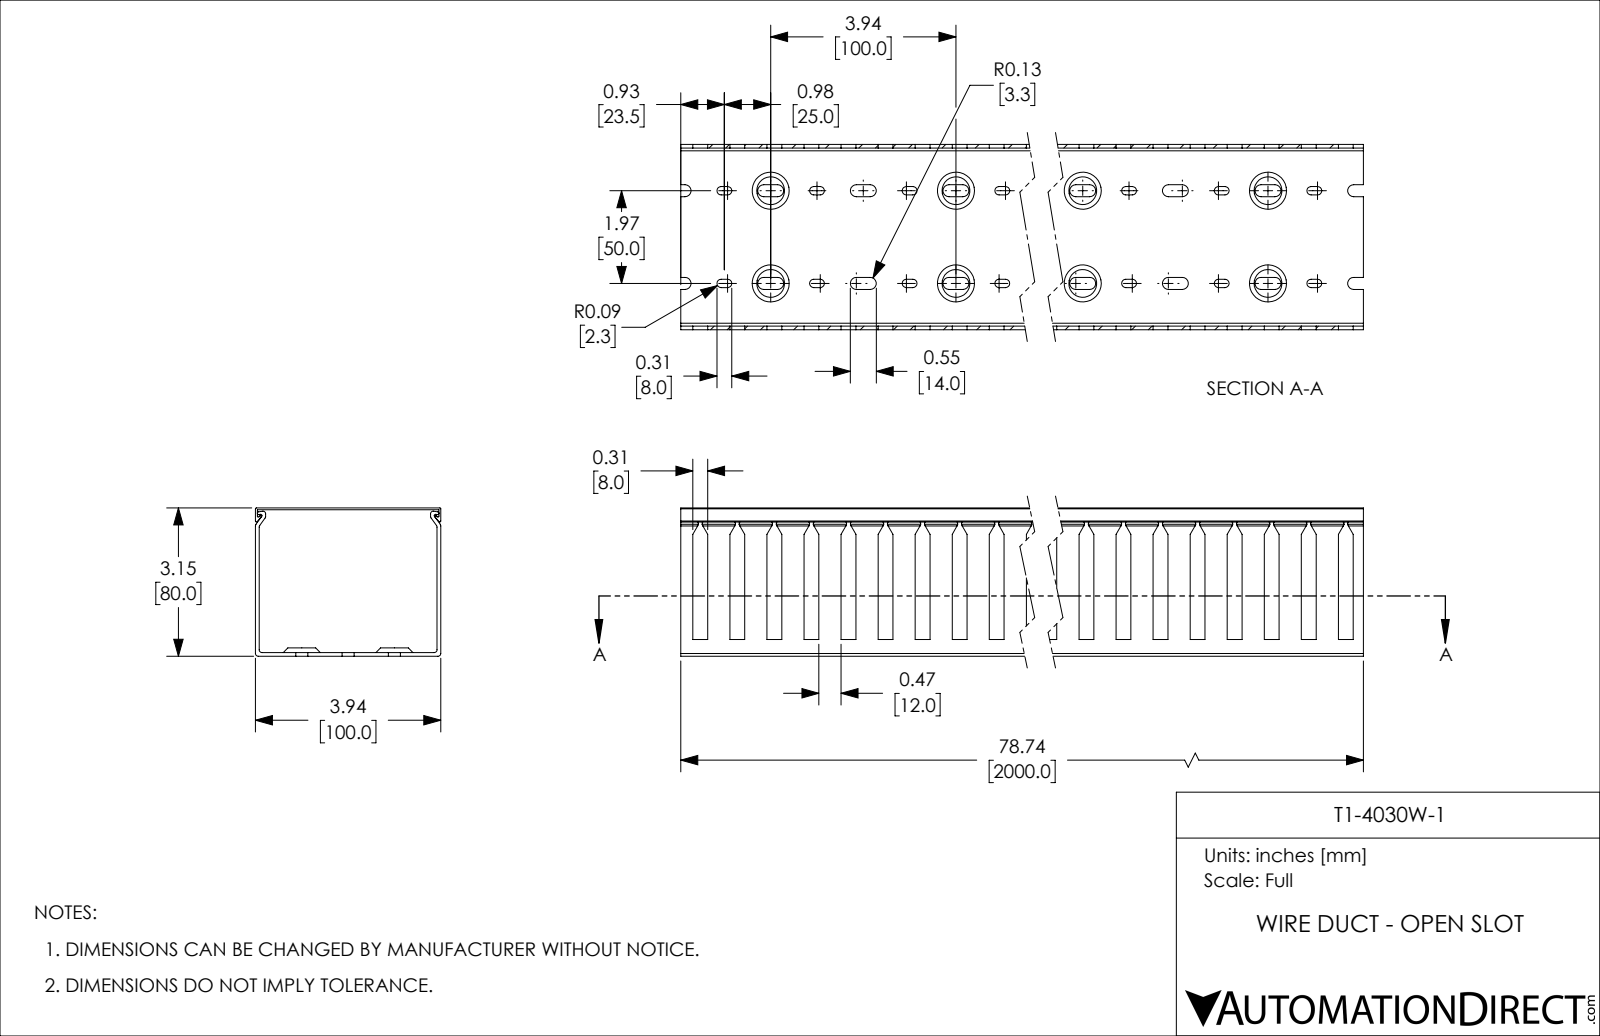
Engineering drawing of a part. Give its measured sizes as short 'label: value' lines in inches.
name: T1-4030W-1
written by: SolidWorks 2021 (CONFIG_CONTROL_DESIGN)
unit: in
bodies: 2 solids, 1573 faces (762 planar, 731 cylindrical, 80 other)
size: 78.74 × 3.937 × 3.15
volume: 75.91 in³; area: 2 300 in²
rounds: 200× R0.128, 160× R0.089, 12× R0.059, 8× R0.02, 6× R0.03
face distances: 0.079, 3.858, 0.039, 3.15, 3.11, 3.031, 3.071, 3.937, 3.78, 3.898
